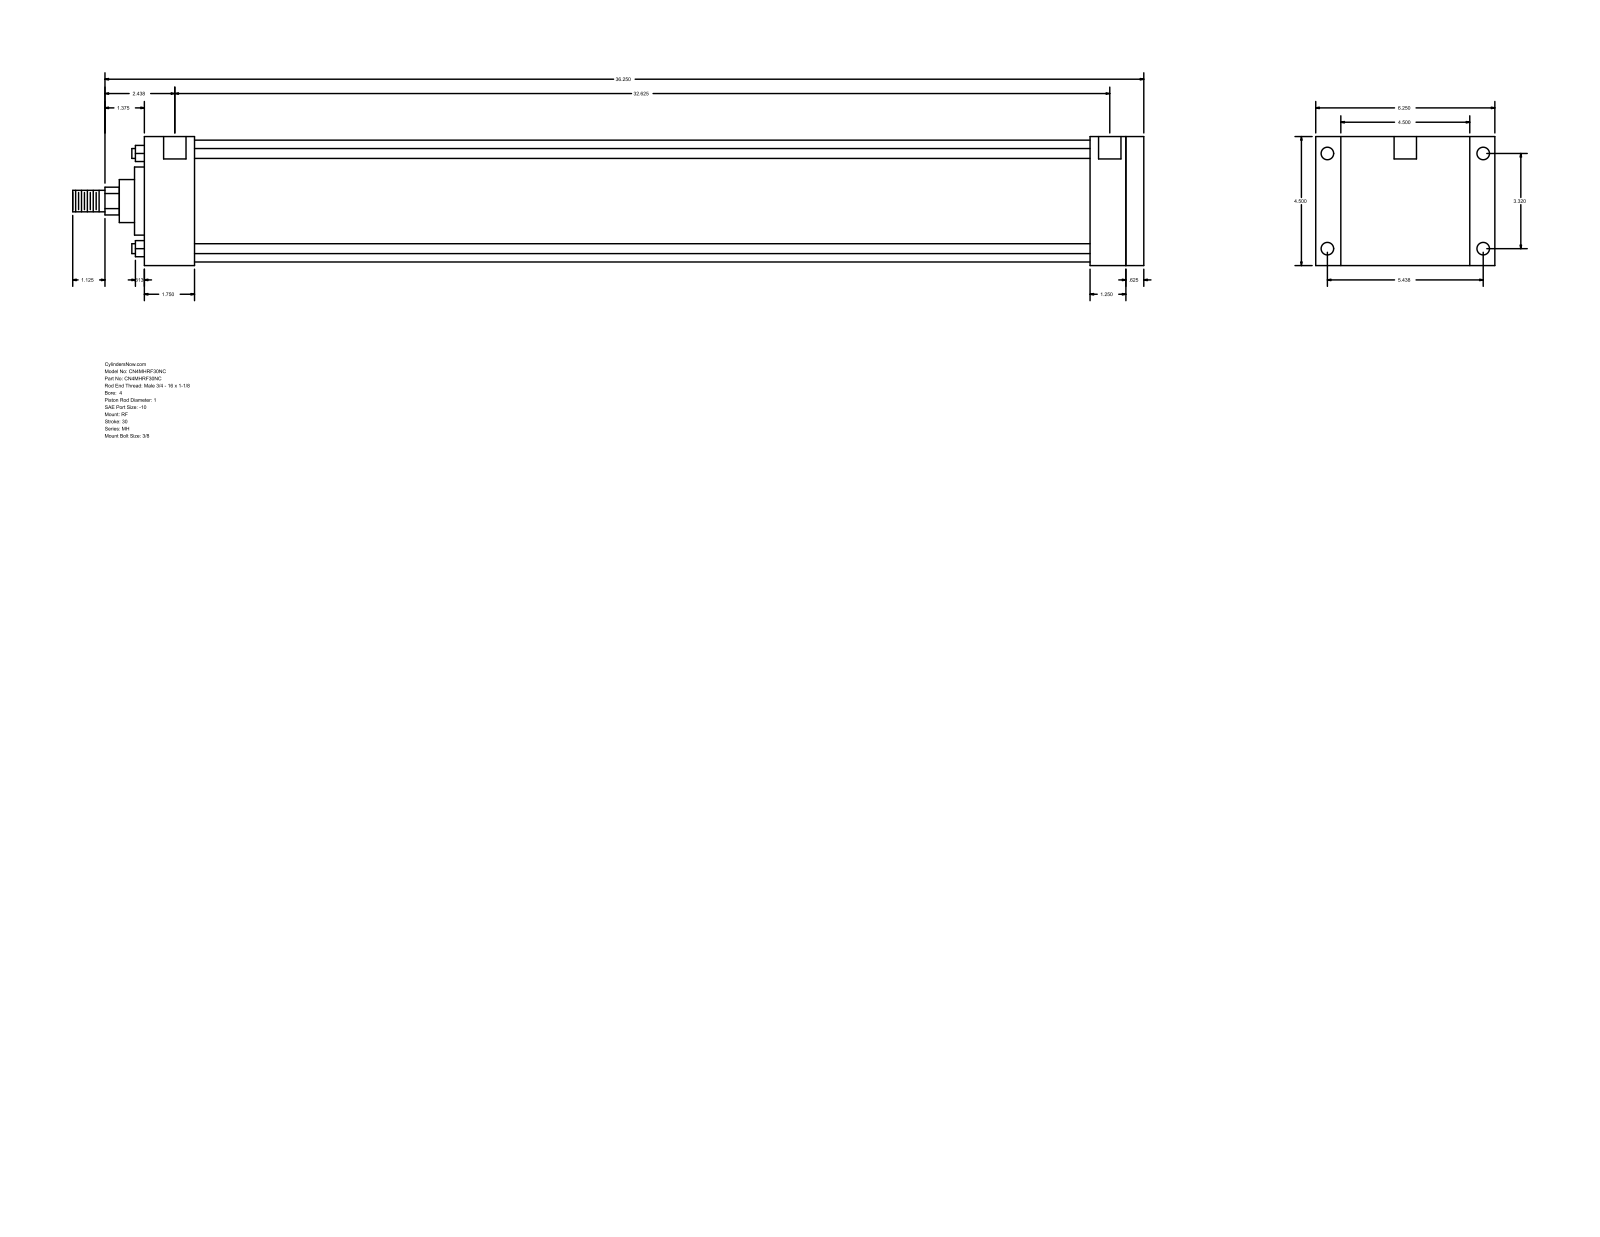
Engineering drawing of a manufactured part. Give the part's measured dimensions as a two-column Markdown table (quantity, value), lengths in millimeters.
| quantity | value |
| --- | --- |
| part name | MH_RF__0400_1 |
| STEP written by | GSSL Pune (CONFIG_CONTROL_DESIGN) |
| units | millimeters |
| bodies | 0 solids, 94 faces (65 planar, 29 cylindrical, 0 other) |
| overall size | 949.33 × 158.75 × 114.3 |
| round holes (diameter × count) | 8.73 × 4, 11.13 × 4, 19.84 × 2 |
| round bosses / shafts (diameter × count) | 8.76 × 4, 107.95 × 1, 60.33 × 1, 38.1 × 1, 25.4 × 1, 19.05 × 1 |
| partial cylindrical surfaces (radius × count) | 12.29 × 1 |
| main face-to-face distances | 114.3, 885.83, 869.96, 15.87, 47.63, 44.46, 825.5, 841.37, 838.2, 793.74 |
| hole center spacings | 1.58, 84.32, 138.12, 161.82, 830.26, 831.84, 828.68 |
